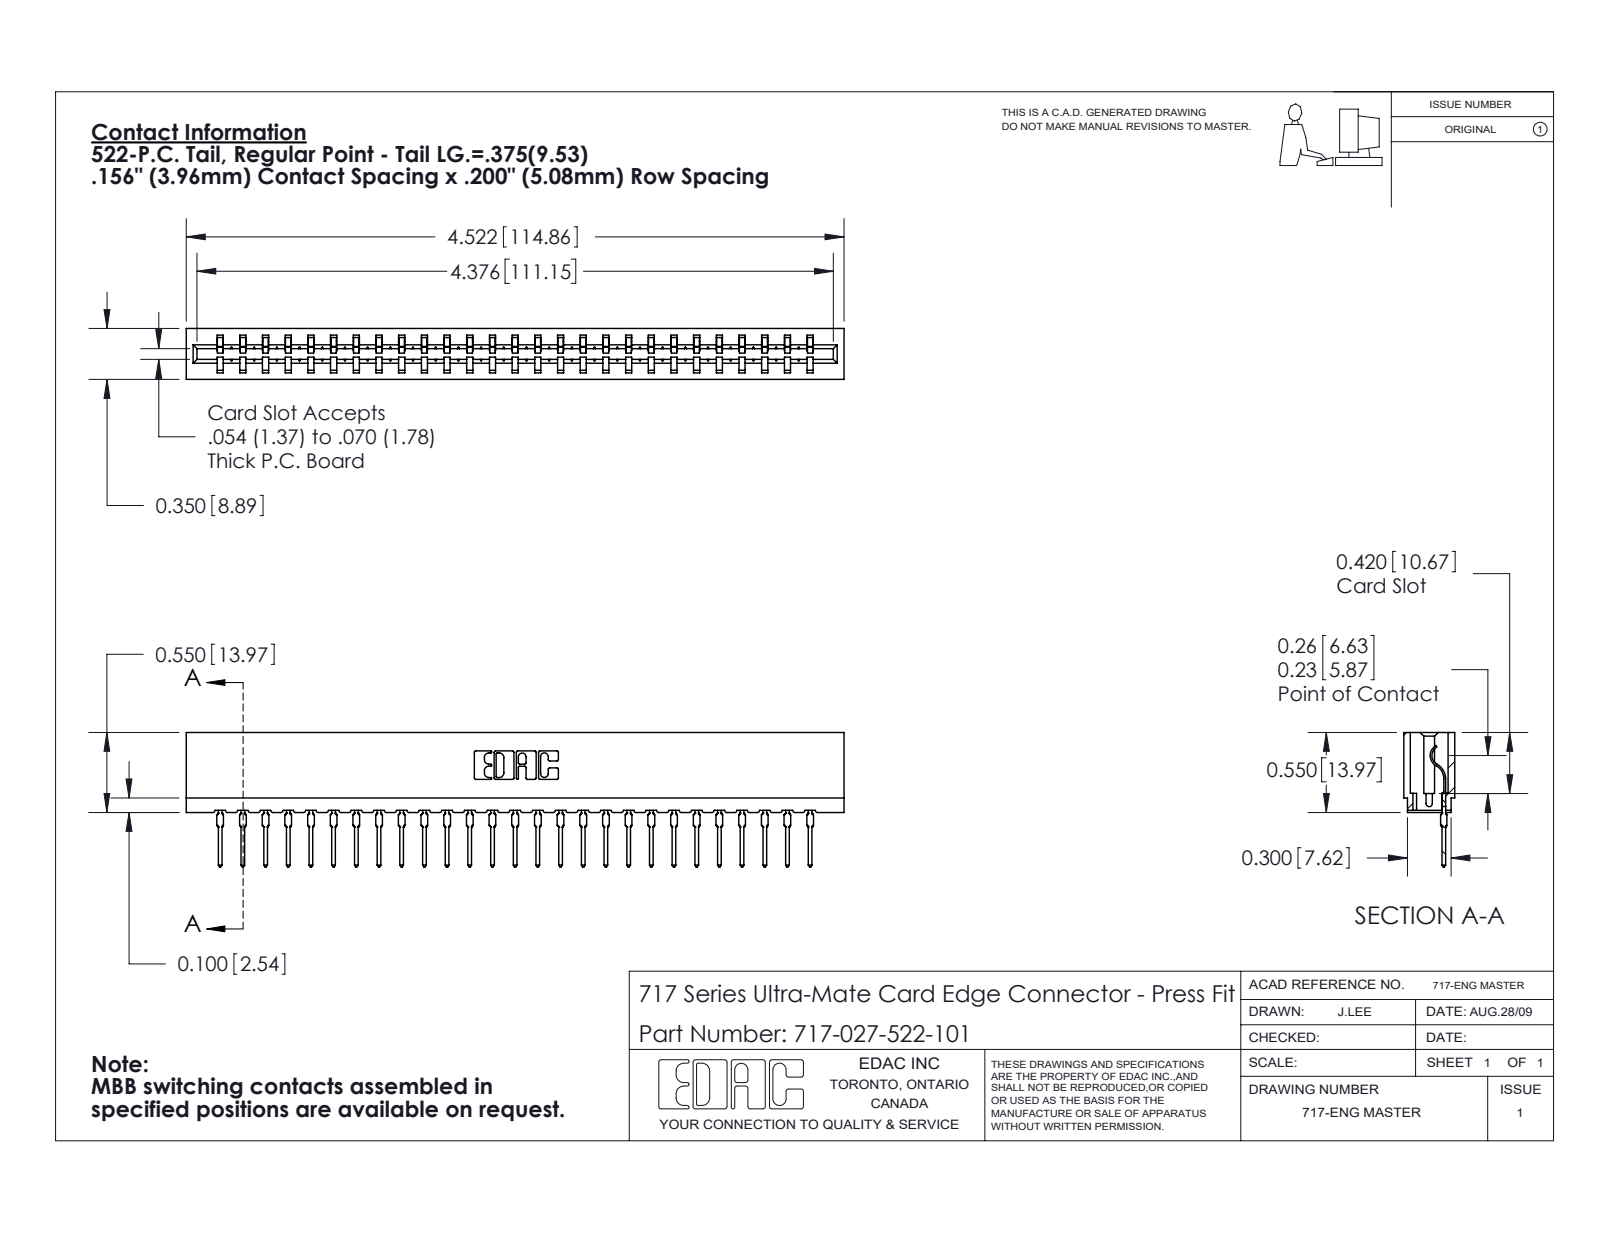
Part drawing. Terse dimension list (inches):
name: 717 Part_Insulator Option - 06; 745-292-001_522; 717-027-522-101
written by: SolidWorks 2020 (CONFIG_CONTROL_DESIGN)
unit: in
bodies: 28 solids, 3145 faces (1890 planar, 553 cylindrical, 702 other)
size: 4.522 × 0.924 × 0.35
volume: 0.597 in³; area: 21.13 in²
rounds: 54× R0.015, 54× R0.021, 22× R0.01, 6× R0.007, 6× R0.031, 4× R0.005, 4× R0.011, 3× R0.026
face distances: 0.212, 0.138, 0.35, 0.156, 0.074, 0.045, 0.305, 0.093, 0.167, 0.063
